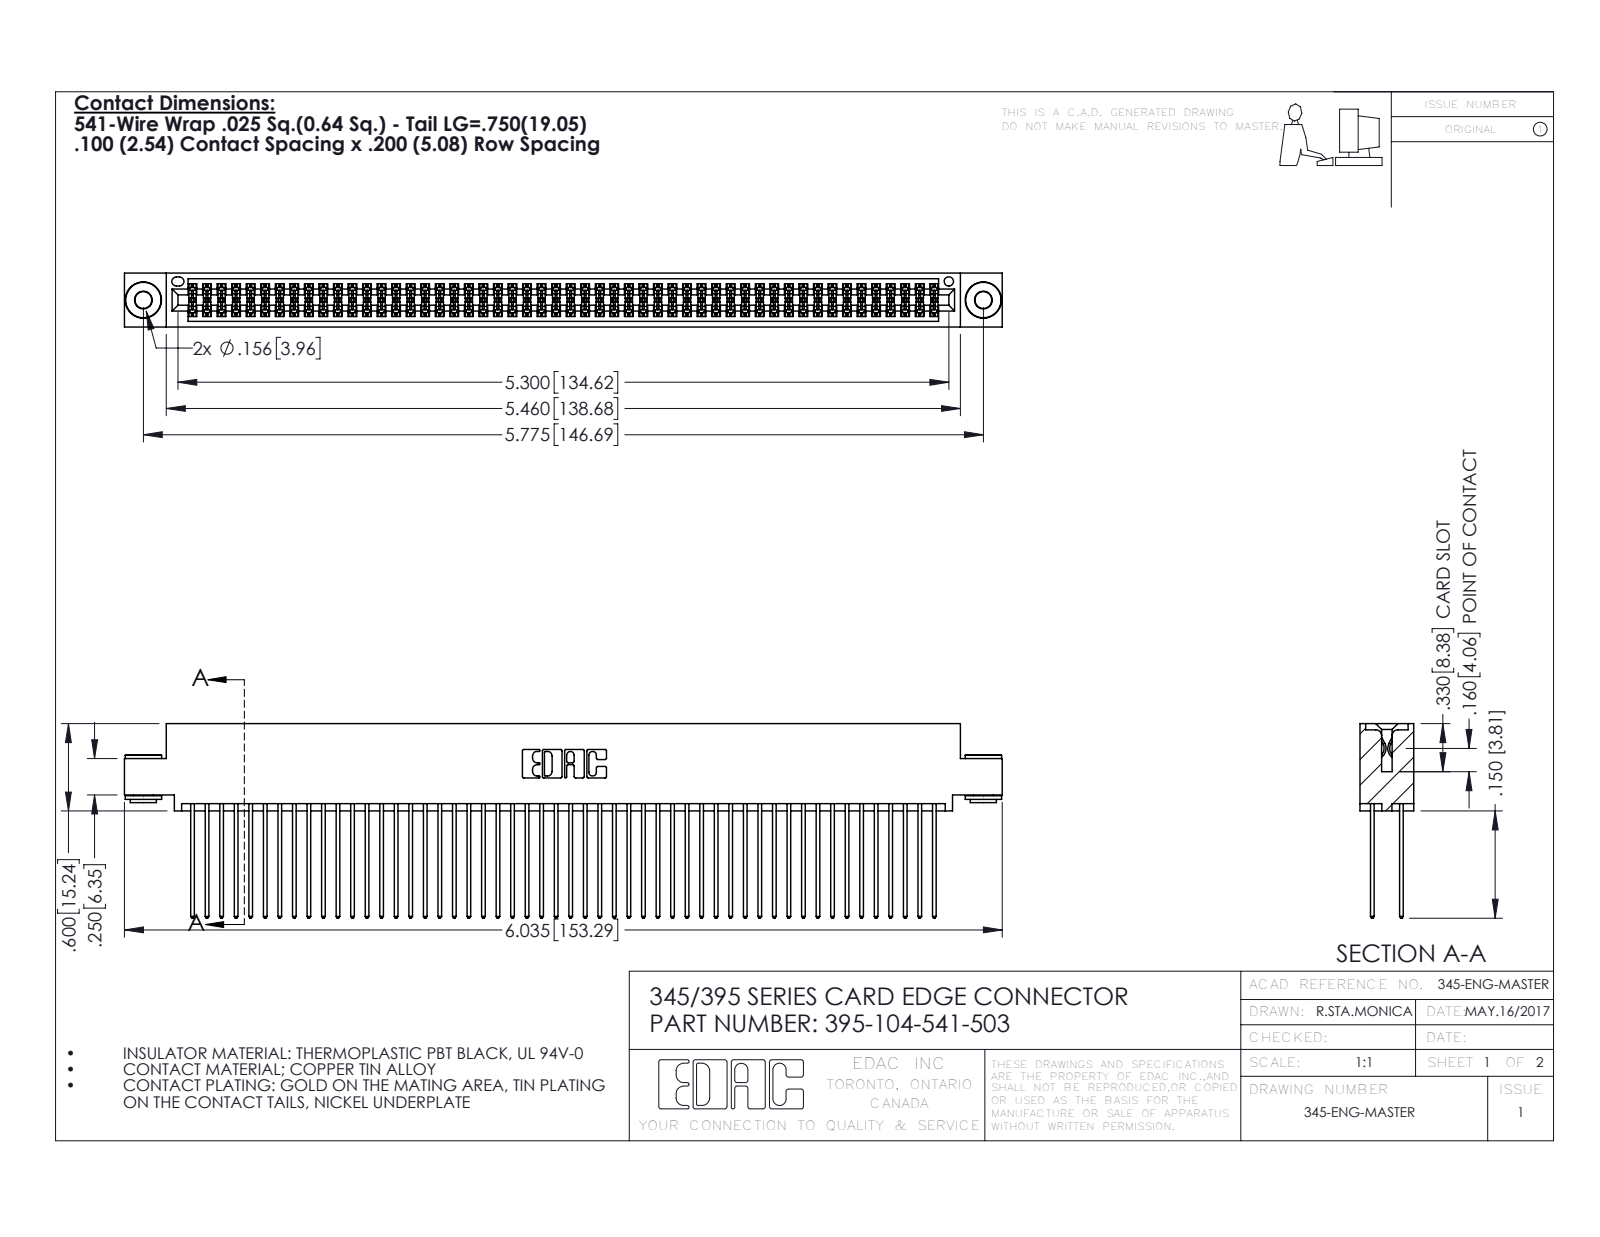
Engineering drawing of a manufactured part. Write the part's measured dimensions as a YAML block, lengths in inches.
part_name: "345-250-002_345-250-002-102; 345-292-001_345-293-141; 345 Part_0.110 Offset - 0.156 Dia-TH; 395-104-541-503"
step_written_by: "SolidWorks 2016 (CONFIG_CONTROL_DESIGN)"
units: inches
bodies: {solids: 107, faces: 5368, planar: 3526, cylindrical: 1834, other: 8}
overall_size: [6.035, 1.337, 0.37]
volume: 0.947
surface_area: 40.68
round_holes:
  - {diameter: 0.116, count: 2}
  - {diameter: 0.156, count: 2}
  - {diameter: 0.064, count: 1}
round_bosses_or_shafts:
  - {diameter: 0.25, count: 2}
  - {diameter: 0.18, count: 2}
  - {diameter: 0.136, count: 2}
partial_cylinders:
  - {radius: 0.006, count: 156}
  - {radius: 0.01, count: 104}
  - {radius: 0.01, count: 22}
  - {radius: 0.007, count: 6}
  - {radius: 0.031, count: 6}
  - {radius: 0.026, count: 3}
  - {radius: 0.014, count: 2}
  - {radius: 0.019, count: 2}
face_to_face_distances: [0.072, 0.298, 0.2, 0.025, 0.098, 0.272, 0.225, 0.37, 0.175, 0.149]
hole_center_spacings: [0.27, 5.539, 5.775]
